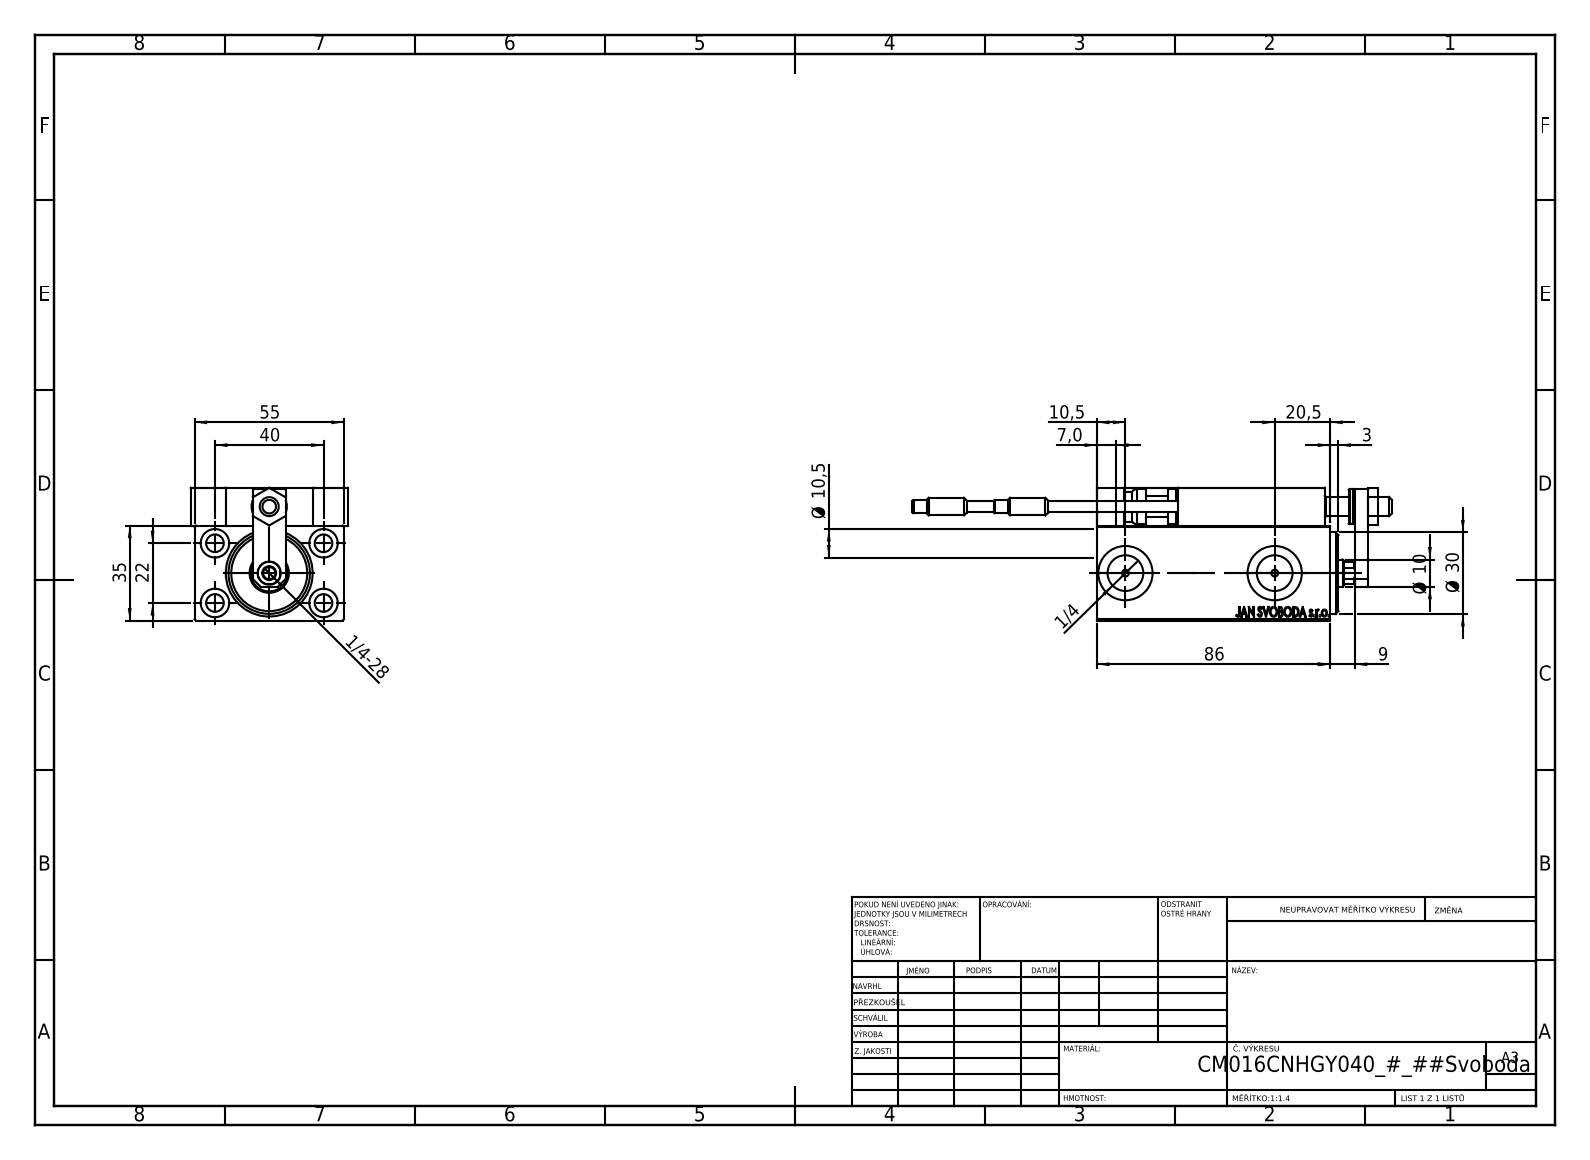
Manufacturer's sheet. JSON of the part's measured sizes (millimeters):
{"part_name": "V450CM_C_VCP; V450CM_VC_B; MAGNET; SWITCH DIM B,W (+7 more)", "step_written_by": "SolidWorks 2019 (CONFIG_CONTROL_DESIGN)", "units": "millimeters", "bodies": {"solids": 23, "faces": 1307, "planar": 563, "cylindrical": 198, "other": 546}, "overall_size": [176.7, 58, 49], "volume_mm3": 188734, "surface_area_mm2": 61676, "round_holes": [[8, 5], [3.2, 4], [4, 4], [6.5, 4], [10.5, 4], [2.5, 2], [5, 2], [13.16, 2], [20, 2], [4.5, 1], [7, 1], [8.5, 1]], "round_bosses_or_shafts": [[5, 4], [6.5, 2], [3.8, 2], [13, 1], [11, 1]], "partial_cylinders_radius": [[0.3, 30], [3, 2], [4.5, 1]], "face_to_face_distances": [35, 14, 5, 49, 55, 7, 3, 10, 1.5, 74], "hole_center_spacings": [22.83, 11.37, 20, 22, 24.13, 29.59, 29.69, 36.06]}
